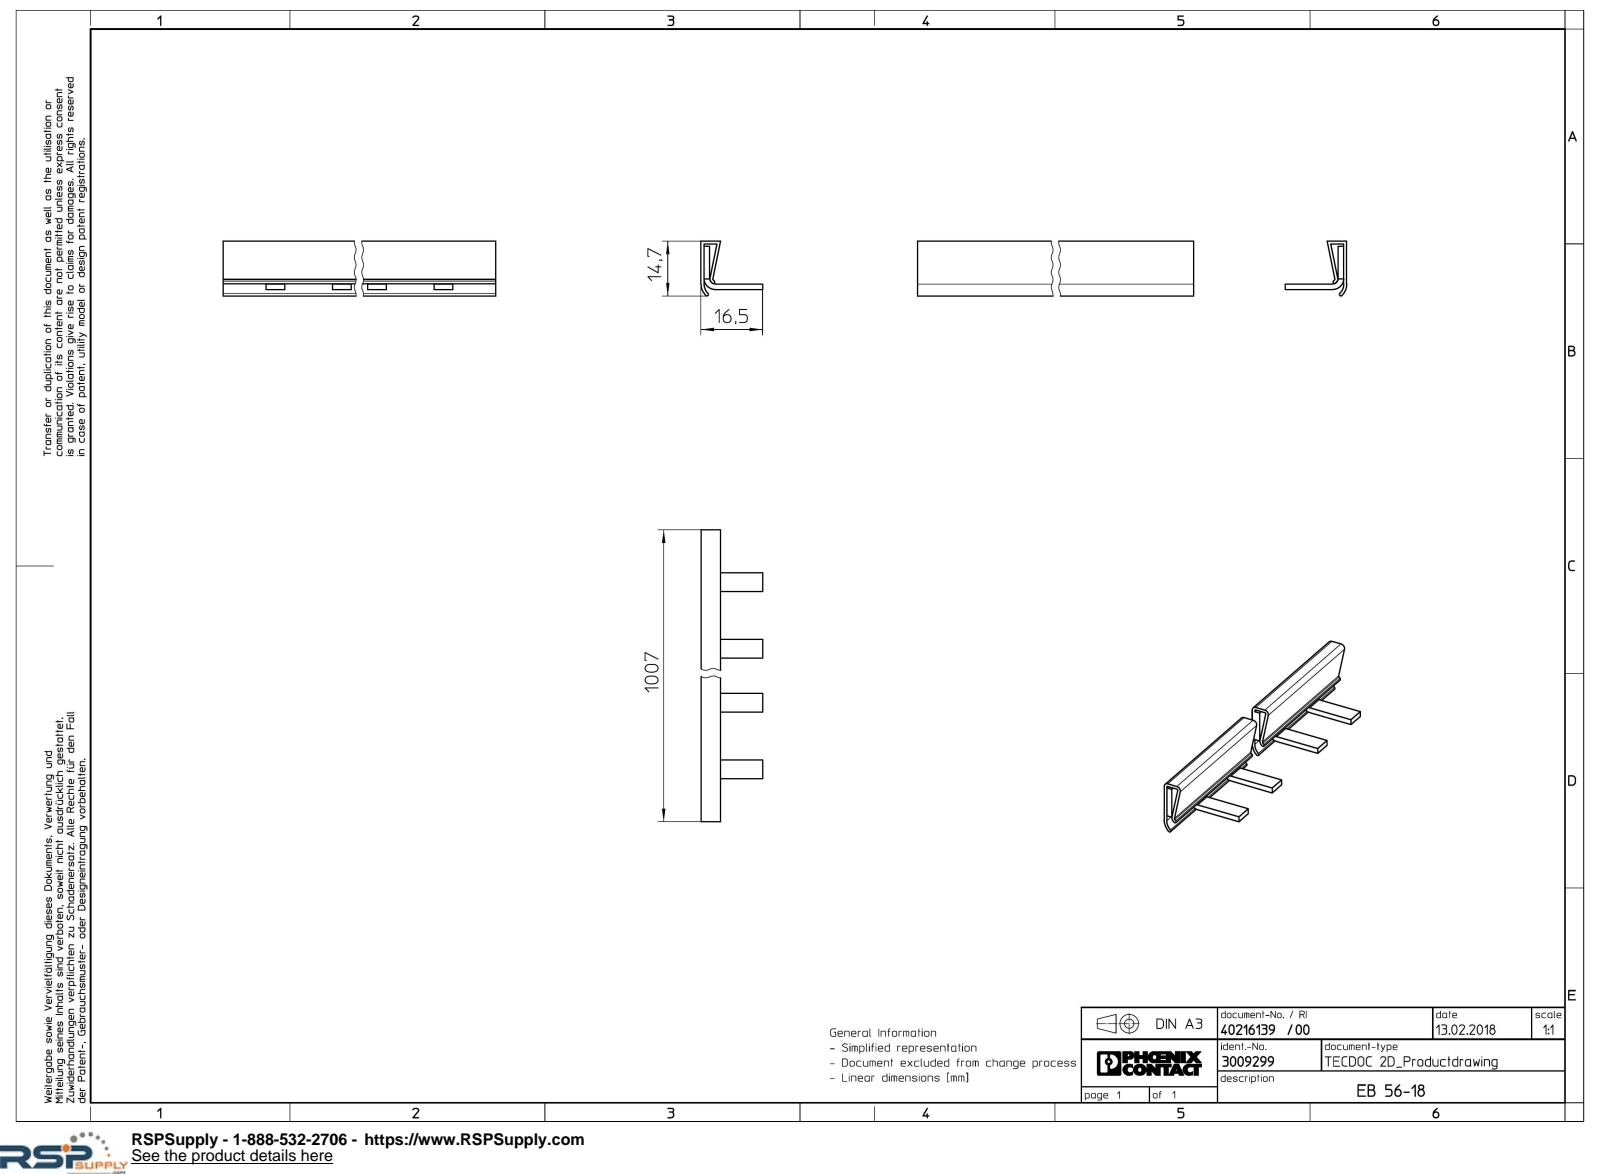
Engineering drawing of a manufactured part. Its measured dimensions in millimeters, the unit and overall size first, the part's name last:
Units: millimetres
Overall size (bounding box): 1007 × 16.5 × 14.7
Partial cylindrical surfaces — rounded edges, fillets, slot ends (radius × count): R0.4 ×2, R1.3 ×1, R1.5 ×1, R3 ×1, R3.5 ×1, R4.3 ×1
Main face-to-face distances: 0.8, 2.3, 1.5, 13, 11.5, 12.2, 10.7, 1.4, 10.1, 11.6
Volume: 44 207 mm³ · Surface area: 76 805 mm²
Bodies: 1 solid, 468 faces (295 planar, 173 cylindrical, 0 other)
Part name (STEP PRODUCT): EB_56_18-select
STEP written by: Creo Elements/Direct Modeling 18.1I 14-Aug-2016 (C) Parametric Technology GmbH (AUTOMOTIVE_DESIGN)
